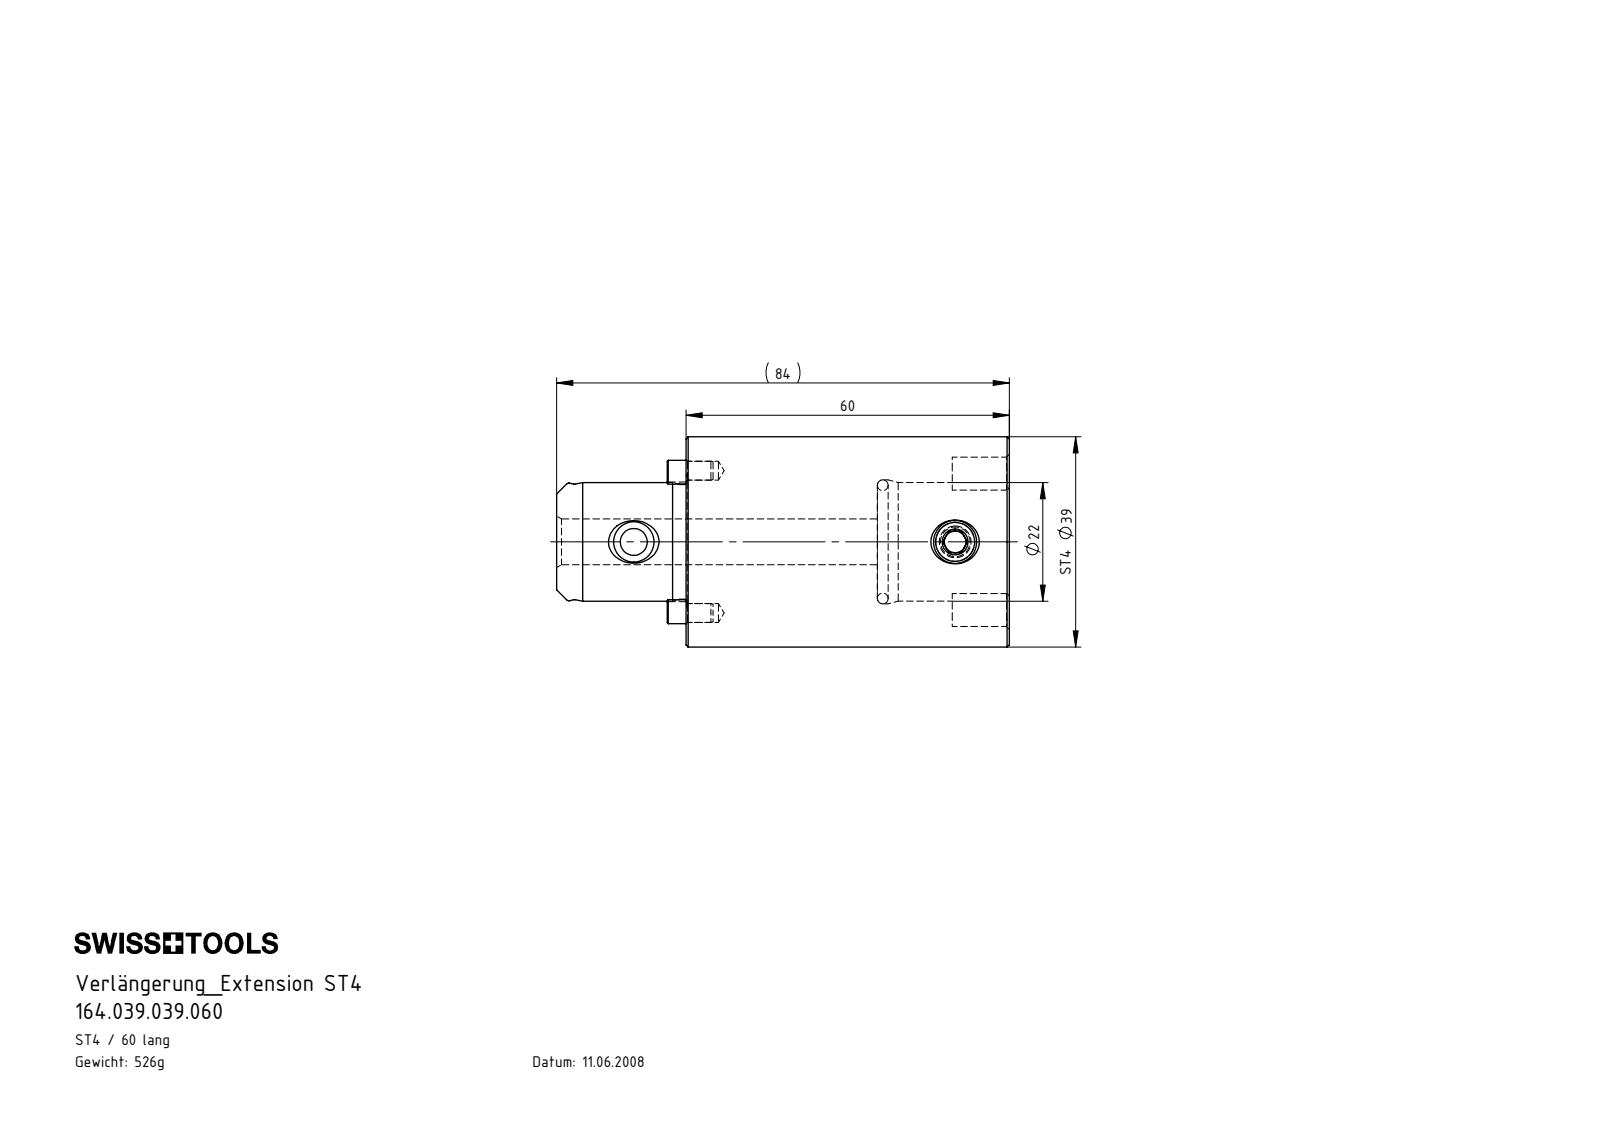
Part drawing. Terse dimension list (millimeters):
name: ST4-ER2.001.009_A; ST4-ER1.001.011_A; ST4-ST4.K01.060; ST4-ST4.K01.060_A (+1 more)
written by: SolidWorks 2015 (CONFIG_CONTROL_DESIGN)
unit: mm
bodies: 5 solids, 154 faces (26 planar, 43 cylindrical, 85 other)
size: 84 × 39 × 39
volume: 67 275 mm³; area: 15 988 mm²
holes: 2× ⌀3.5, 1× ⌀5, 1× ⌀7.25, 1× ⌀8.5, 1× ⌀22, 1× ⌀23
bosses: 1× ⌀39, 1× ⌀21.8, 1× ⌀21.3, 1× ⌀8
rounds: 4× R0.5, 2× R3.2, 2× R3.48, 2× R11.05
face distances: 60, 35.5, 24.5, 24, 59.5, 84, 18.9, 73.4, 49.4, 13.9
hole spacings: 13.2, 26.4, 59.65
